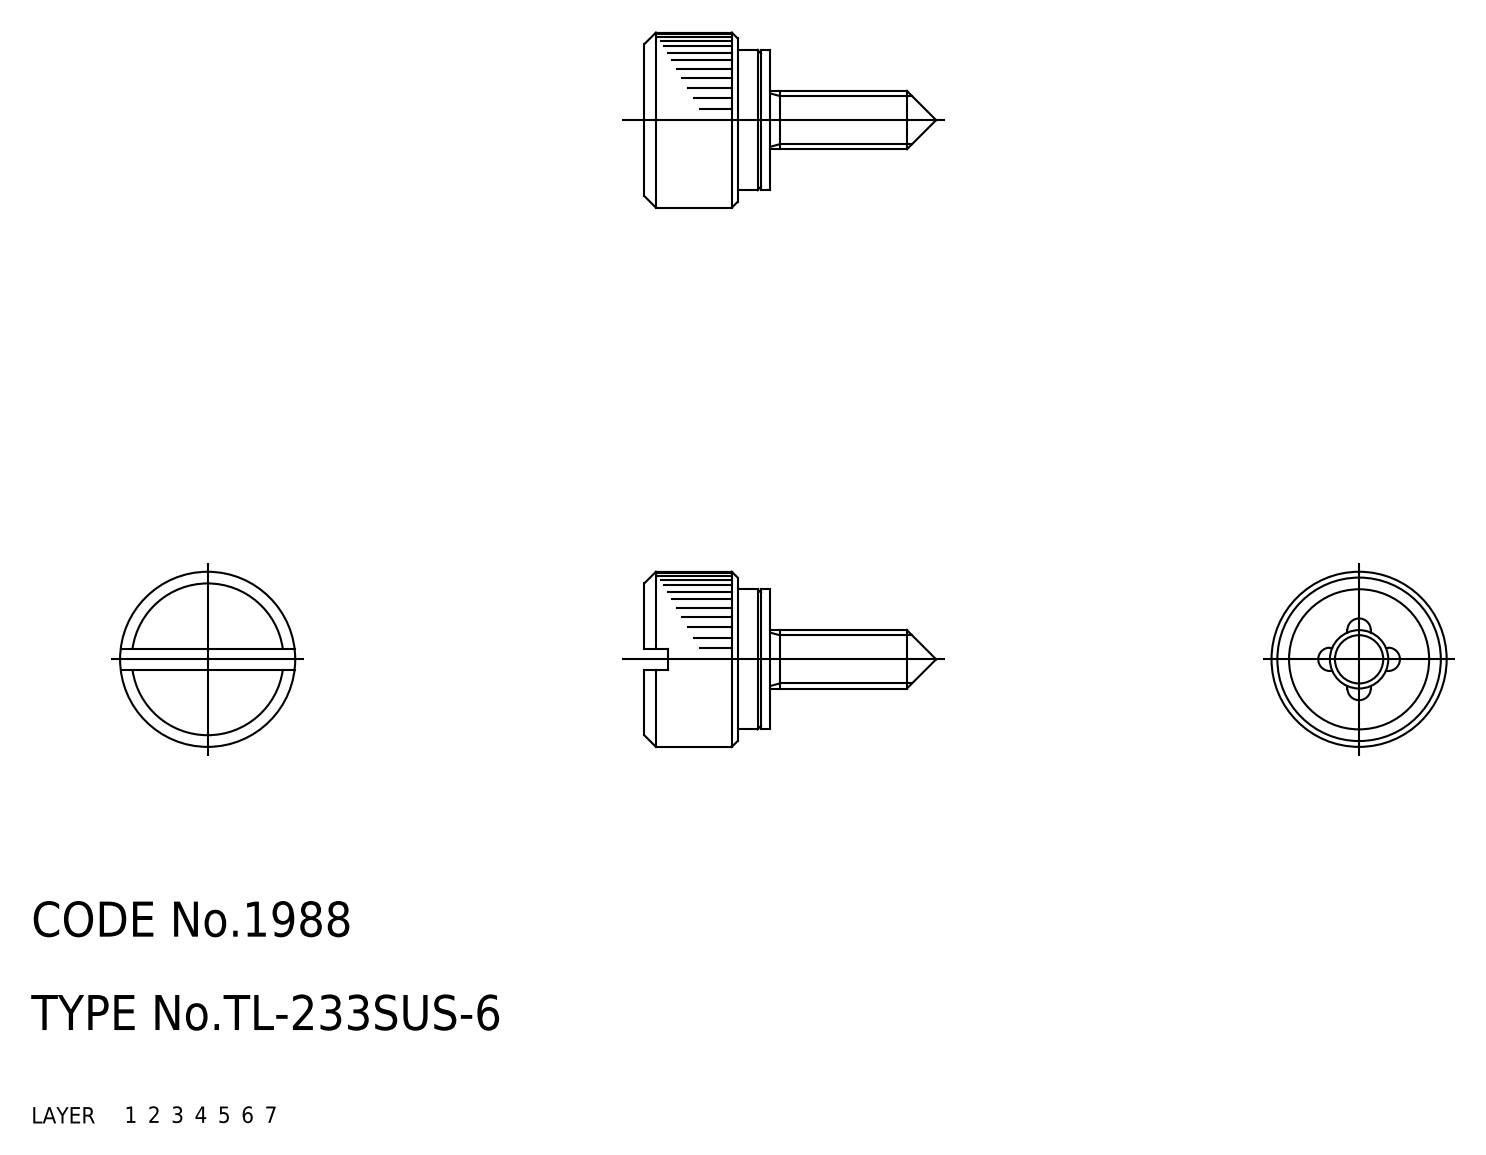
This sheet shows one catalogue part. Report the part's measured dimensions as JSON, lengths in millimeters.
{"part_name": "washer; knob; TL_233SUS_6_29711_36", "step_written_by": "CADfix (AUTOMOTIVE_DESIGN)", "units": "millimeters", "bodies": {"solids": 2, "faces": 41, "planar": 0, "cylindrical": 0, "other": 41}, "overall_size": [25, 15, 15], "volume_mm3": 1893, "surface_area_mm2": 1234}
